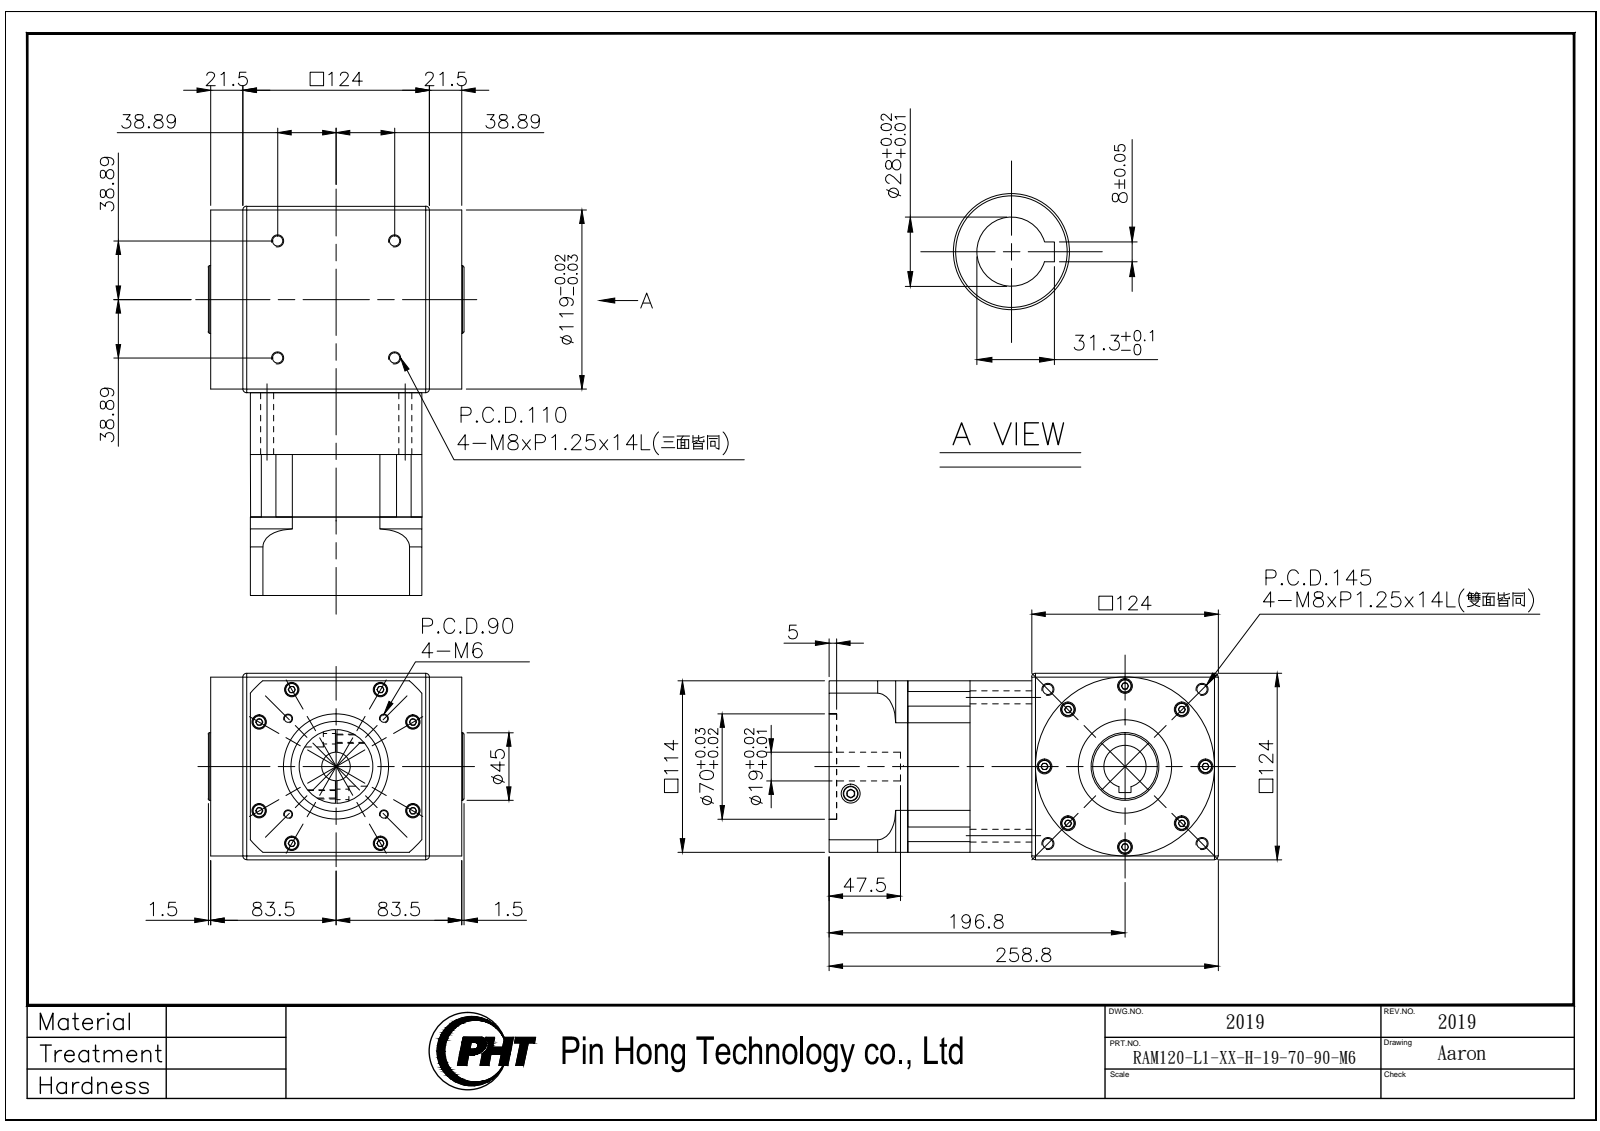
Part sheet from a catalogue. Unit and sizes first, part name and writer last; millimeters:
Units: millimetres
Overall size (bounding box): 258.8 × 170 × 124
Round holes (diameter × count): ⌀6.8 ×12, ⌀5.3 ×8, ⌀9 ×8, ⌀9.5 ×8, ⌀14 ×8, ⌀5 ×4, ⌀8.6 ×4, ⌀12.7 ×2, ⌀19 ×1, ⌀28 ×1, ⌀28.3 ×1, ⌀60 ×1
Round bosses / shafts (diameter × count): ⌀13 ×12, ⌀8.5 ×8, ⌀119 ×1, ⌀110 ×1, ⌀62 ×1, ⌀49 ×1, ⌀45 ×1
Partial cylindrical surfaces — rounded edges, fillets, slot ends (radius × count): R7 ×4, R64 ×1, R75 ×1, R86.2 ×1
Main face-to-face distances: 124, 5, 119, 41.5, 114, 82.5, 41, 206.5, 165, 140.5
Hole centre spacings: 59, 10, 15.4, 17.24, 19.42, 39.8, 51.28, 52
Volume: 3 819 000 mm³ · Surface area: 324 352 mm²
Bodies: 4 solids, 844 faces (424 planar, 272 cylindrical, 148 other)
Part name (STEP PRODUCT): RAM120-L1-XX-H-19-70-90-M6_2019
STEP written by: SolidWorks 2016 (AUTOMOTIVE_DESIGN)
